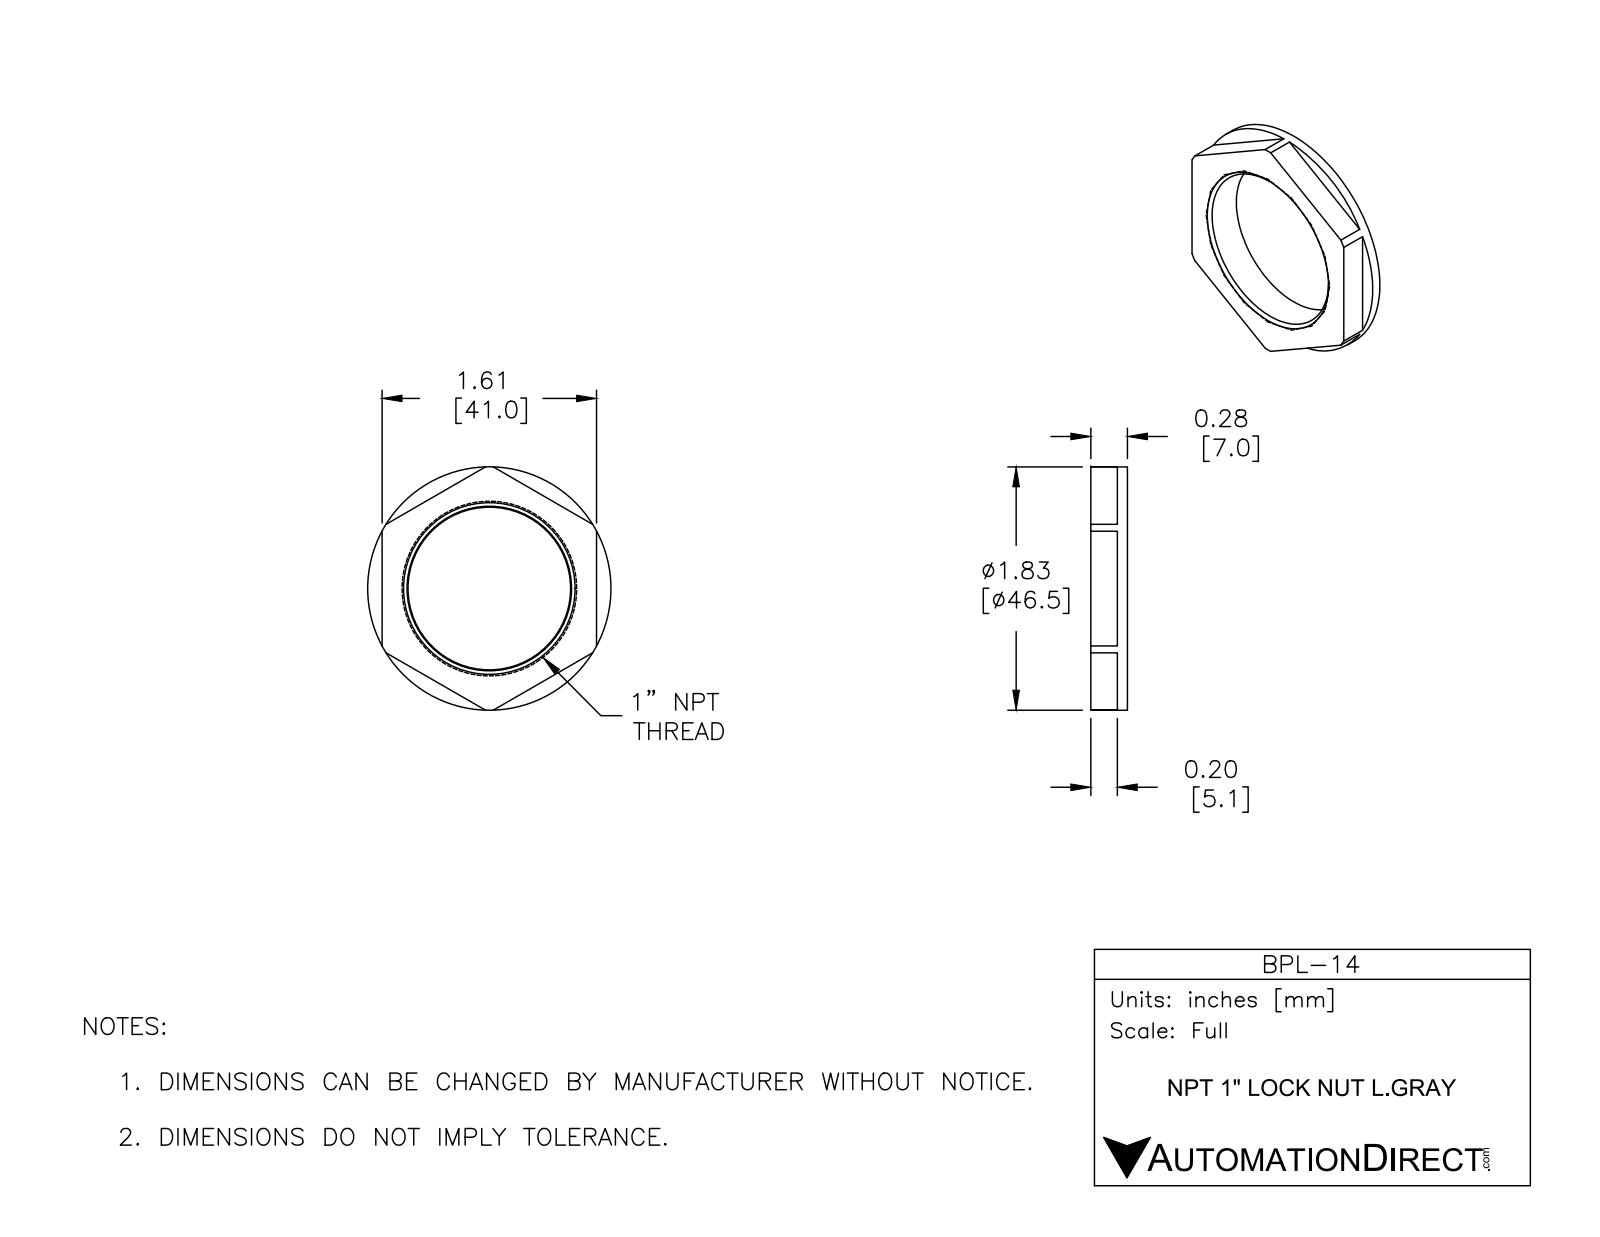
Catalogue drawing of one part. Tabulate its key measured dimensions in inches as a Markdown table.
| quantity | value |
| --- | --- |
| part name | BPL-14 |
| STEP written by | SolidWorks 2015 (CONFIG_CONTROL_DESIGN) |
| units | inches |
| bodies | 1 solid, 20 faces (14 planar, 2 cylindrical, 4 other) |
| overall size | 1.83 × 1.83 × 0.276 |
| volume | 0.32 in³ |
| surface area | 5.434 in² |
| round bosses / shafts (diameter × count) | 1.83 × 1 |
| main face-to-face distances | 0.276, 1.614, 0.076, 0.2 |
